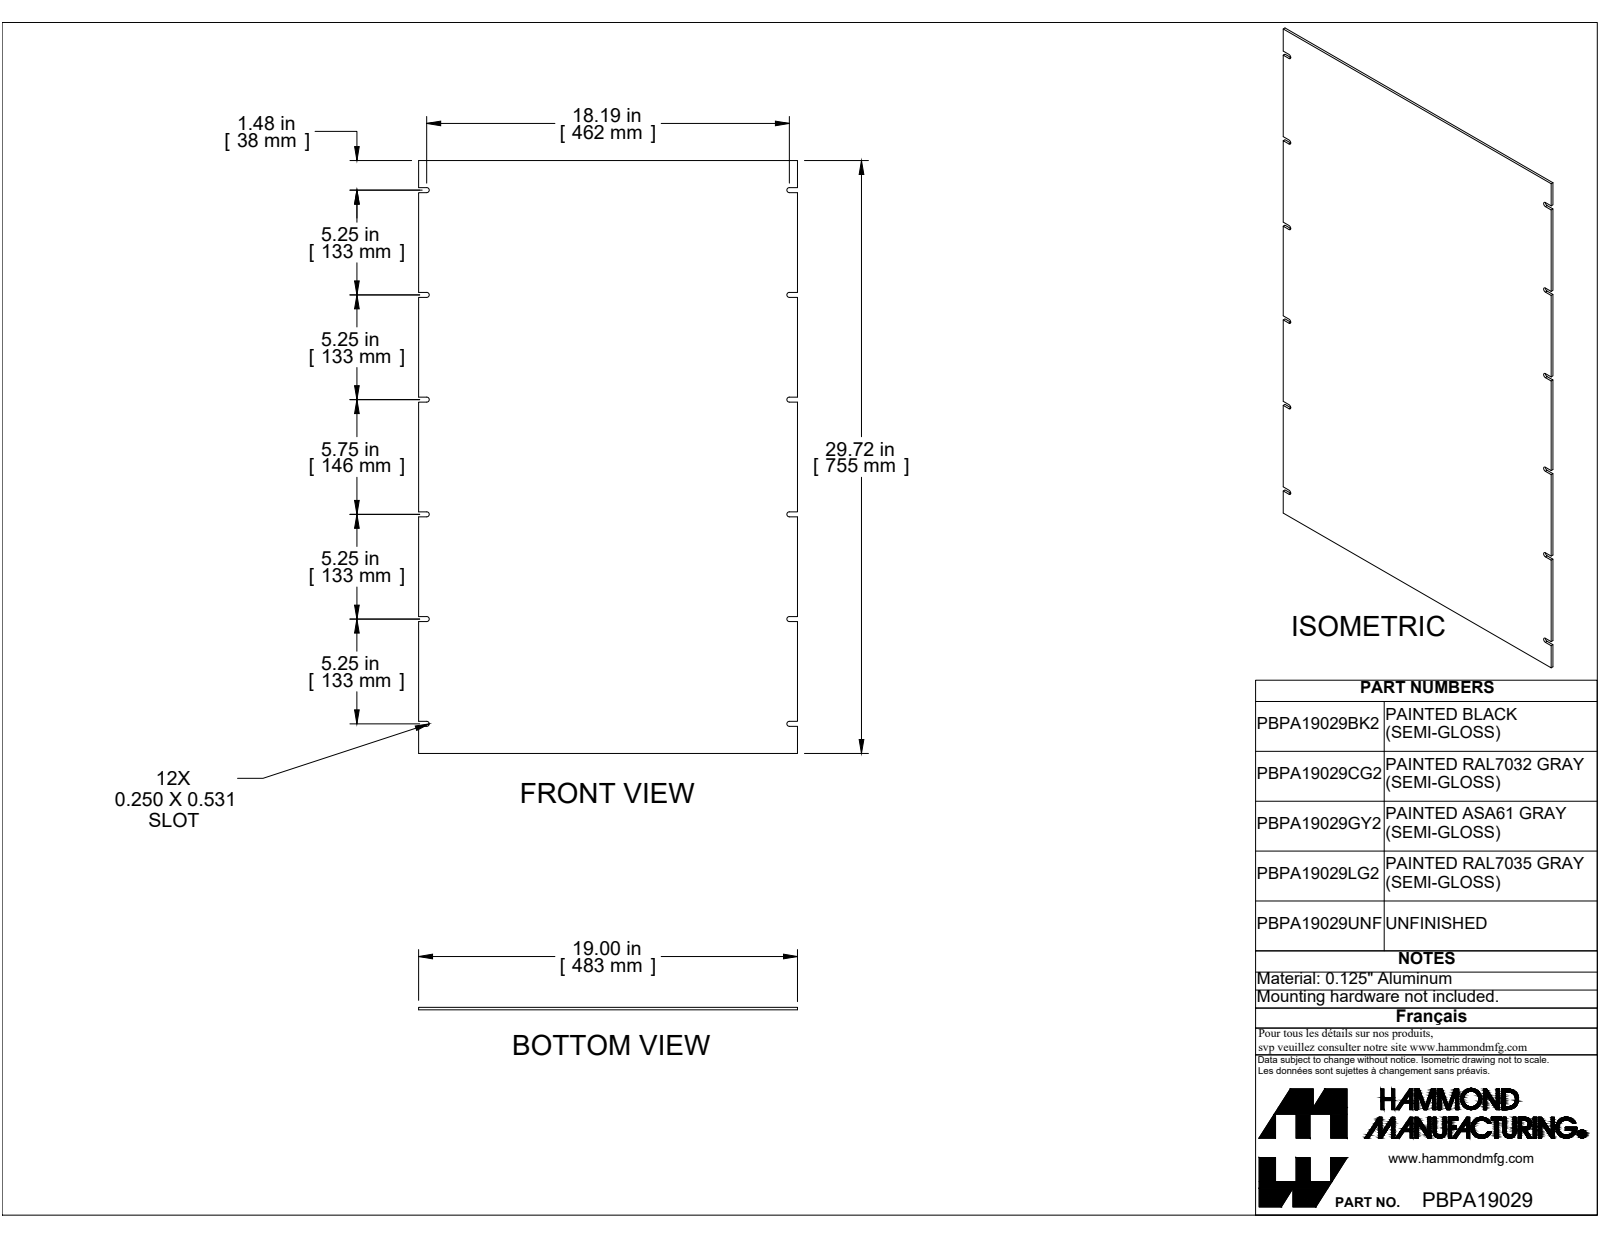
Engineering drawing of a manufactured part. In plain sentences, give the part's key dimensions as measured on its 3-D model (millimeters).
The part is named "PBPA19029LG2". Its 3-D file was written by "SolidWorks 2019 (CONFIG_CONTROL_DESIGN)". It is 1 solid with 54 faces: 42 planar, 12 cylindrical and 0 other. Overall it measures 754.8 by 482.6 by 3.2 millimeters. Its volume is 1 153 000 cubic millimeters and its surface area 735 500 square millimeters. Partial cylindrical surfaces (rounded edges, fillets, slot ends): 12 of radius 3.2. The main face-to-face distances are 3.2, 482.6, 754.8, 133.4, 412.8, 6.4, 139.7, 266.7, 546.1, 279.4.
